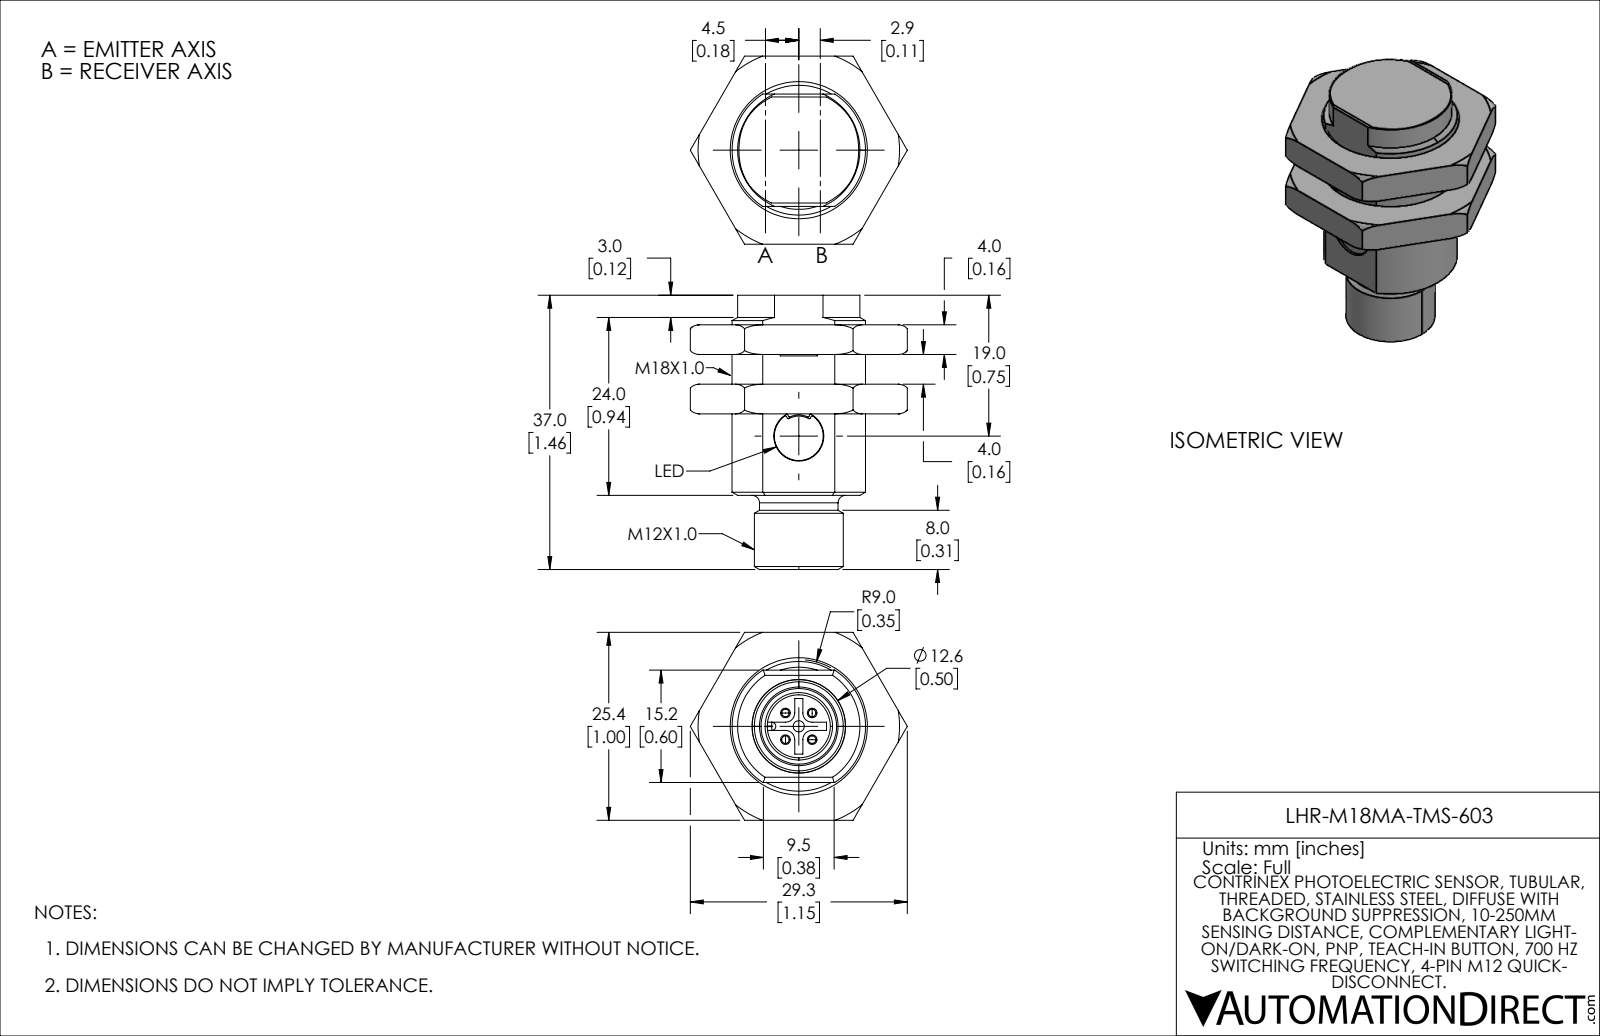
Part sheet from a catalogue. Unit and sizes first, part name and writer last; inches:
Units: inches
Overall size (bounding box): 1.457 × 1.153 × 0.998
Round holes (diameter × count): ⌀0.059 ×1, ⌀0.266 ×1, ⌀0.335 ×1, ⌀0.689 ×1
Round bosses / shafts (diameter × count): ⌀0.039 ×4, ⌀0.472 ×1, ⌀0.417 ×1
Partial cylindrical surfaces — rounded edges, fillets, slot ends (radius × count): R0.004 ×4, R0.006 ×4, R0.049 ×4, R0.02 ×2, R0.022 ×1, R0.106 ×1, R0.112 ×1, R0.325 ×1
Main face-to-face distances: 0.157, 0.315, 0.472, 0.998, 0.201, 0.798, 0.597, 0.63, 0.433, 0.591
Volume: 0.572 in³ · Surface area: 7.737 in²
Bodies: 3 solids, 177 faces (66 planar, 50 cylindrical, 61 other)
Part name (STEP PRODUCT): LHR-M18MA-TMS-603
STEP written by: SolidWorks 2021 (AUTOMOTIVE_DESIGN)
